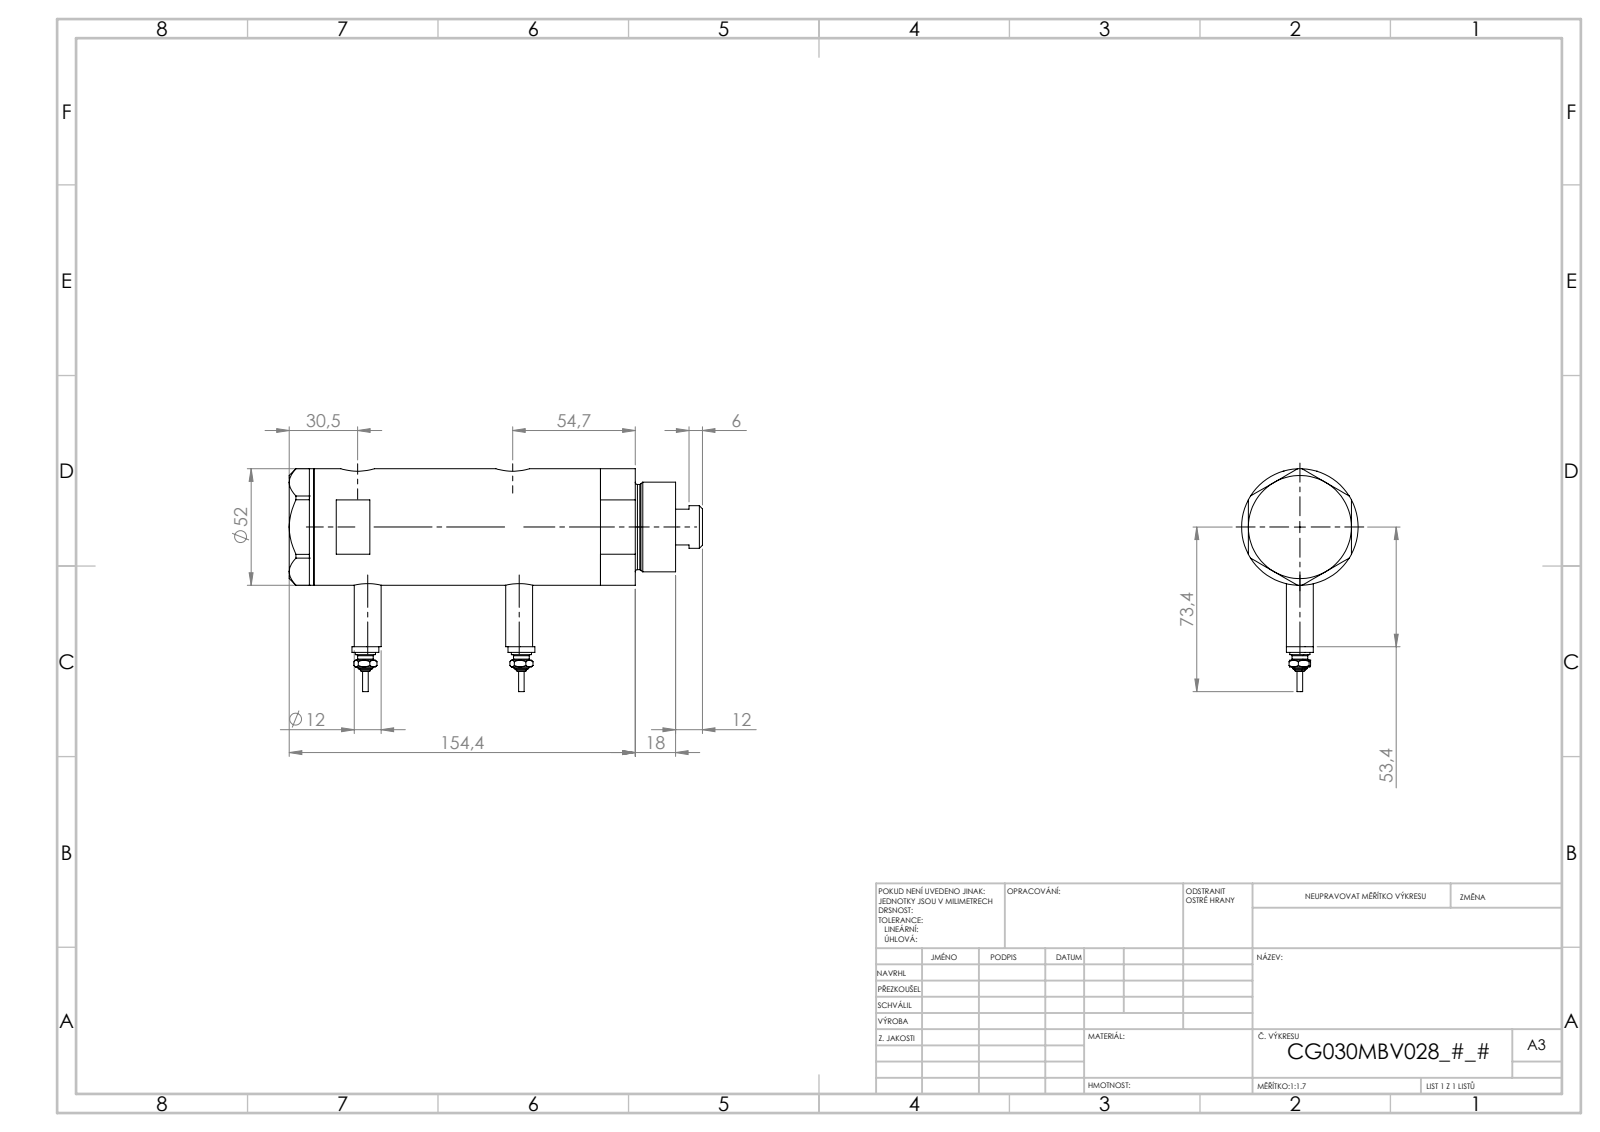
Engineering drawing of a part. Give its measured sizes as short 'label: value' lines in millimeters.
name: V270CG_VC; V270CG_BACK; V270CG_MIDDLE; V270CG_FRONT (+1 more)
written by: SolidWorks 2019 (CONFIG_CONTROL_DESIGN)
unit: mm
bodies: 6 solids, 226 faces (93 planar, 69 cylindrical, 64 other)
size: 184.4 × 99.4 × 52
volume: 341 720 mm³; area: 79 976 mm²
holes: 2× ⌀9.73, 2× ⌀12.5, 2× ⌀15, 1× ⌀6.5, 1× ⌀20, 1× ⌀21.5, 1× ⌀30, 1× ⌀33, 1× ⌀44
bosses: 4× ⌀12, 2× ⌀9, 2× ⌀7, 2× ⌀4.5, 2× ⌀2.5, 1× ⌀52, 1× ⌀40, 1× ⌀38
face distances: 91.5, 23.8, 67.7, 11, 34.8, 102.5, 46, 36.4, 138.9, 127.9
hole spacings: 2.9, 4.5, 64.7, 67.6, 69.2, 72.1
